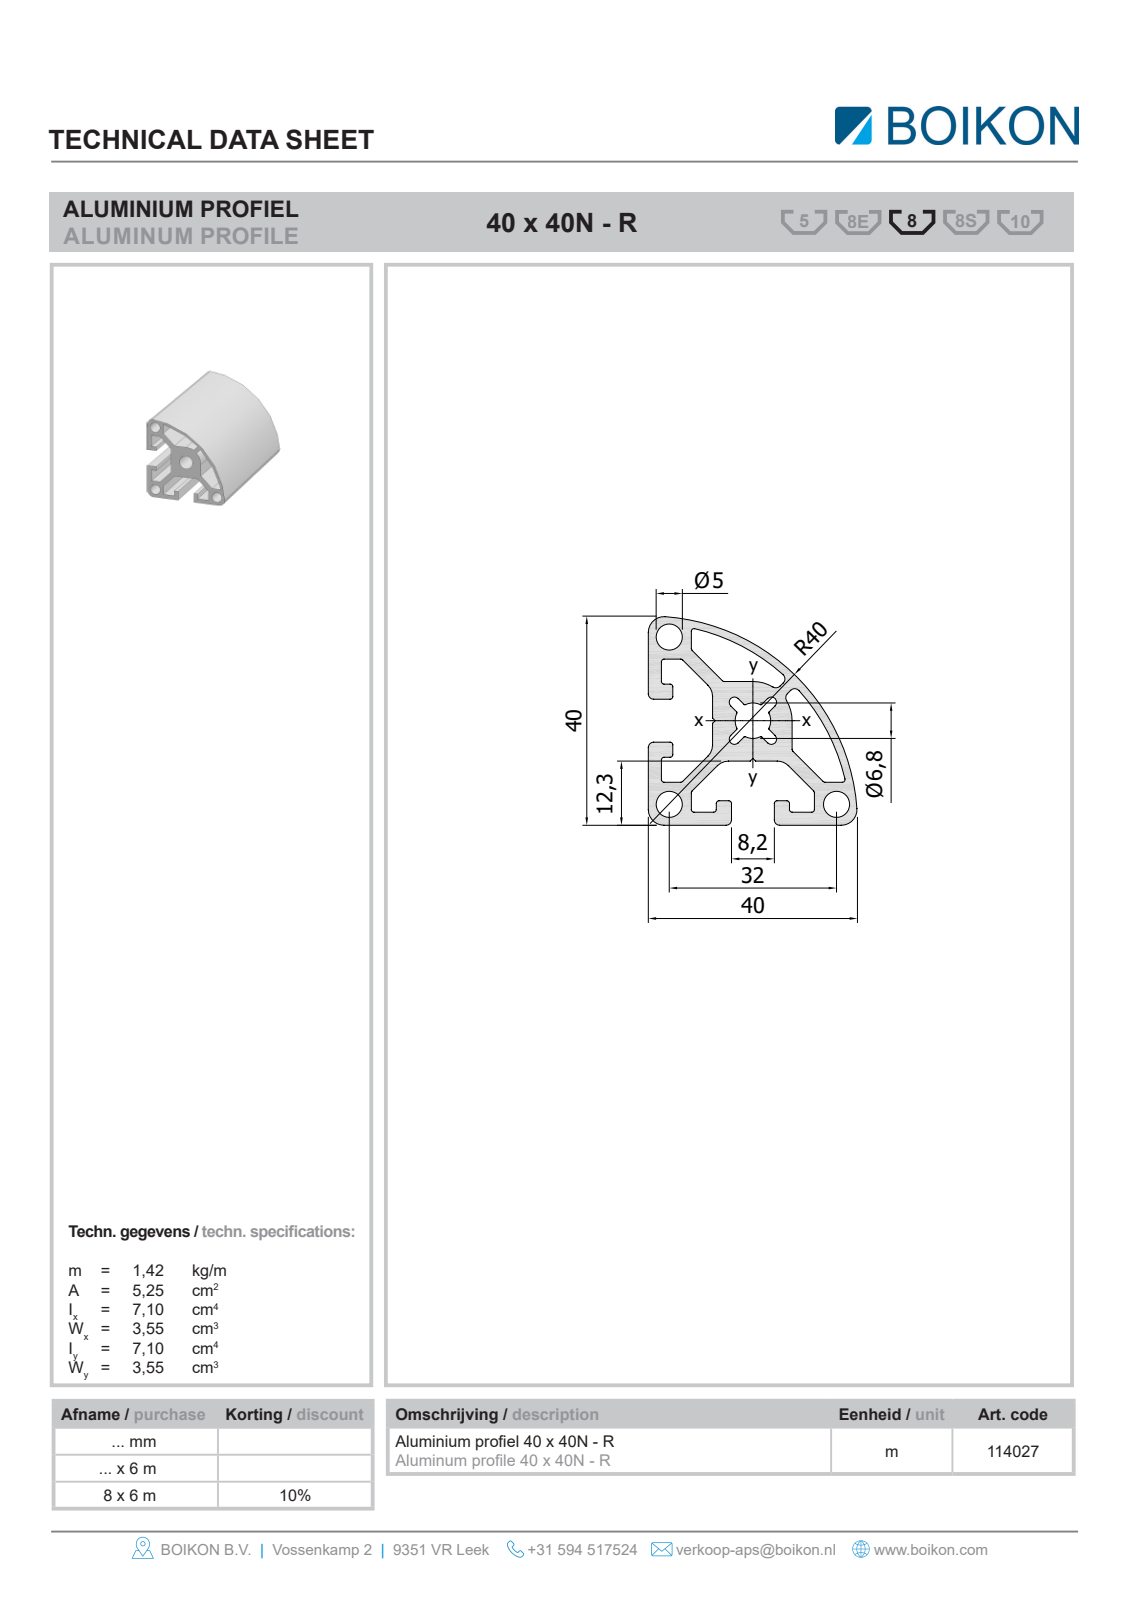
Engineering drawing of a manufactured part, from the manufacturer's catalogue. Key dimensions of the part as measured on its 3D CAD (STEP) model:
Part name (STEP PRODUCT): Root; 11402740x40N-RBOIKON0
STEP written by: HiCAD 2013 1802.4 Build 509 (AUTOMOTIVE_DESIGN)
Units: millimetres
Bodies: 1 solid, 52 faces (40 planar, 12 cylindrical, 0 other)
Overall size (bounding box): 1000 × 40 × 39.97
Volume: 520 635 mm³ · Surface area: 421 122 mm²
Round holes (diameter × count): ⌀5 ×3, ⌀6.8 ×1
Partial cylindrical surfaces — rounded edges, fillets, slot ends (radius × count): R3 ×3, R7.43 ×1, R7.76 ×1, R38.77 ×1, R38.82 ×1, R40 ×1
Main face-to-face distances: 2, 2.5, 4, 12.25, 10.25, 19.5, 3.65, 11.85, 7.65, 15.85
Hole centre spacings: 22.63, 32, 45.25
